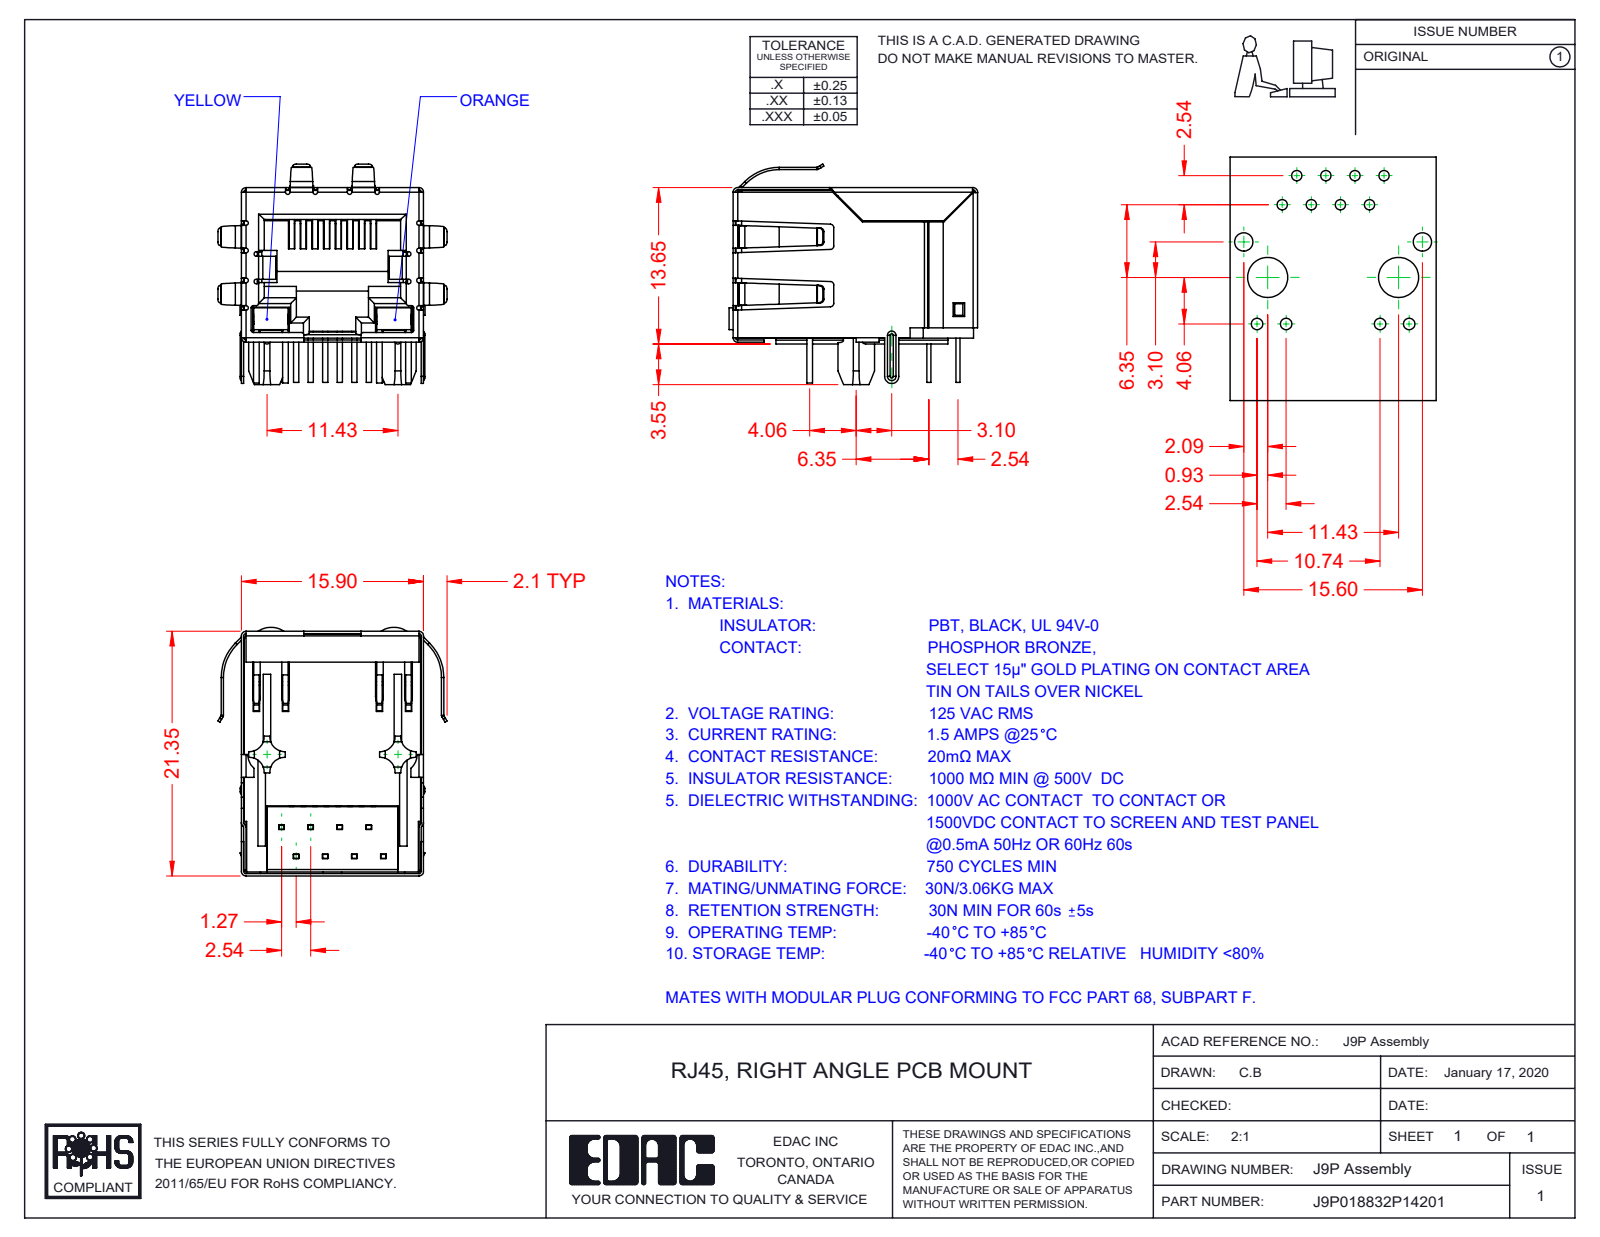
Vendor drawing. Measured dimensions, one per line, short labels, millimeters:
name: 9P-LED Insulator; 9P-LED Shield; 9P-LED LED LH_1-Yellow; 9P-LED Assembly (+4 more)
written by: SolidWorks 2016 (CONFIG_CONTROL_DESIGN)
unit: mm
bodies: 13 solids, 1472 faces (1042 planar, 336 cylindrical, 94 other)
size: 21.7 × 20 × 19.25
volume: 2 687 mm³; area: 7 515 mm²
rounds: 39× R0.2, 22× R0.5, 20× R0.3, 16× R0.4, 8× R1.3, 5× R0.23, 4× R0.11, 4× R0.31
face distances: 15.45, 15.7, 15.65, 0.35, 0.54, 15.5, 12.36, 0.6, 1.4, 0.59
